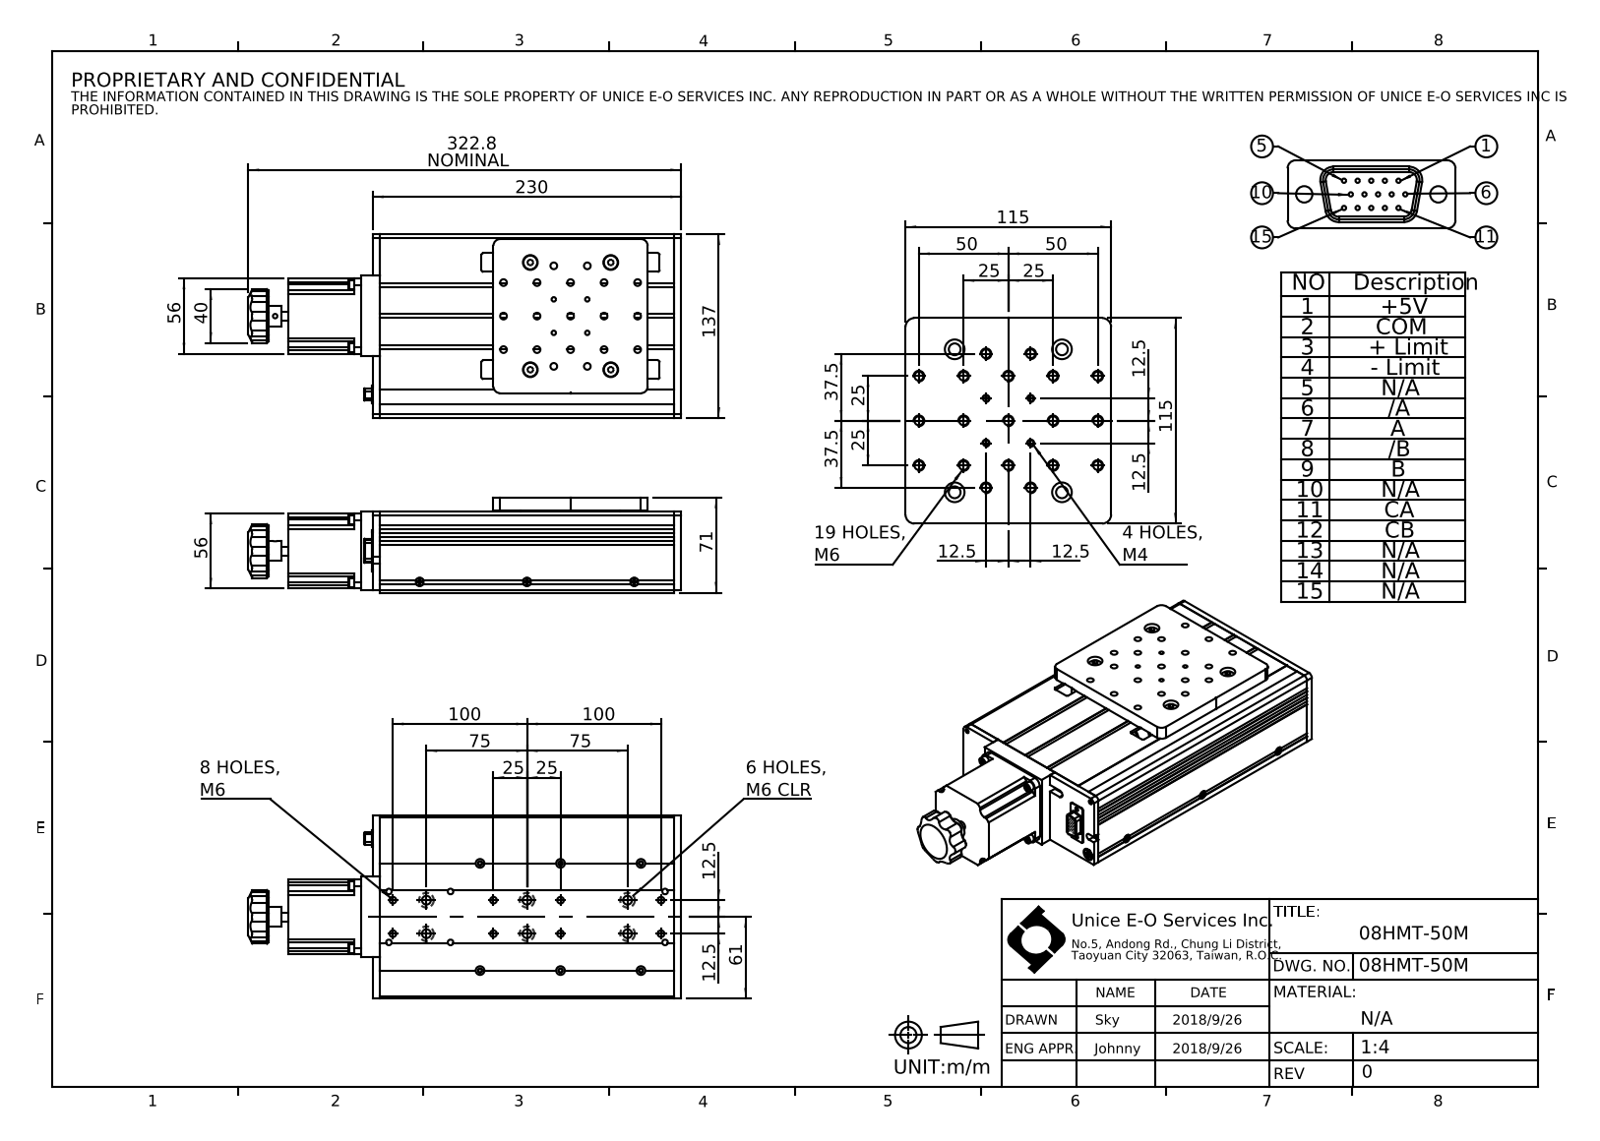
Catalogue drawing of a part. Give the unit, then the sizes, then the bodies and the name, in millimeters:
Units: millimetres
Overall size (bounding box): 322.8 × 137 × 71
Round holes (diameter × count): ⌀5 ×27, ⌀0.8 ×15, ⌀3.3 ×6, ⌀4.2 ×6, ⌀6.5 ×6, ⌀6.6 ×6, ⌀11 ×6, ⌀2 ×2, ⌀2.26 ×2, ⌀3.05 ×2, ⌀25 ×1
Round bosses / shafts (diameter × count): ⌀6.5 ×4, ⌀5.8 ×3, ⌀7.7 ×2, ⌀7 ×2, ⌀15 ×1, ⌀14 ×1, ⌀6.35 ×1
Partial cylindrical surfaces — rounded edges, fillets, slot ends (radius × count): R0.5 ×8, R4 ×8, R5 ×8, R7.41 ×8, R1.5 ×5, R2 ×4, R4.5 ×4, R3 ×3
Main face-to-face distances: 2, 135, 60.5, 1.5, 133, 10.5, 59, 5, 71, 225
Hole centre spacings: 39.53, 25, 17.68, 55.9, 35.36, 50, 63.74, 2.84
Bodies: 0 solids, 729 faces (348 planar, 270 cylindrical, 111 other)
Part name (STEP PRODUCT): 08HMT-50M
STEP written by: SolidWorks 2016 (AUTOMOTIVE_DESIGN)
